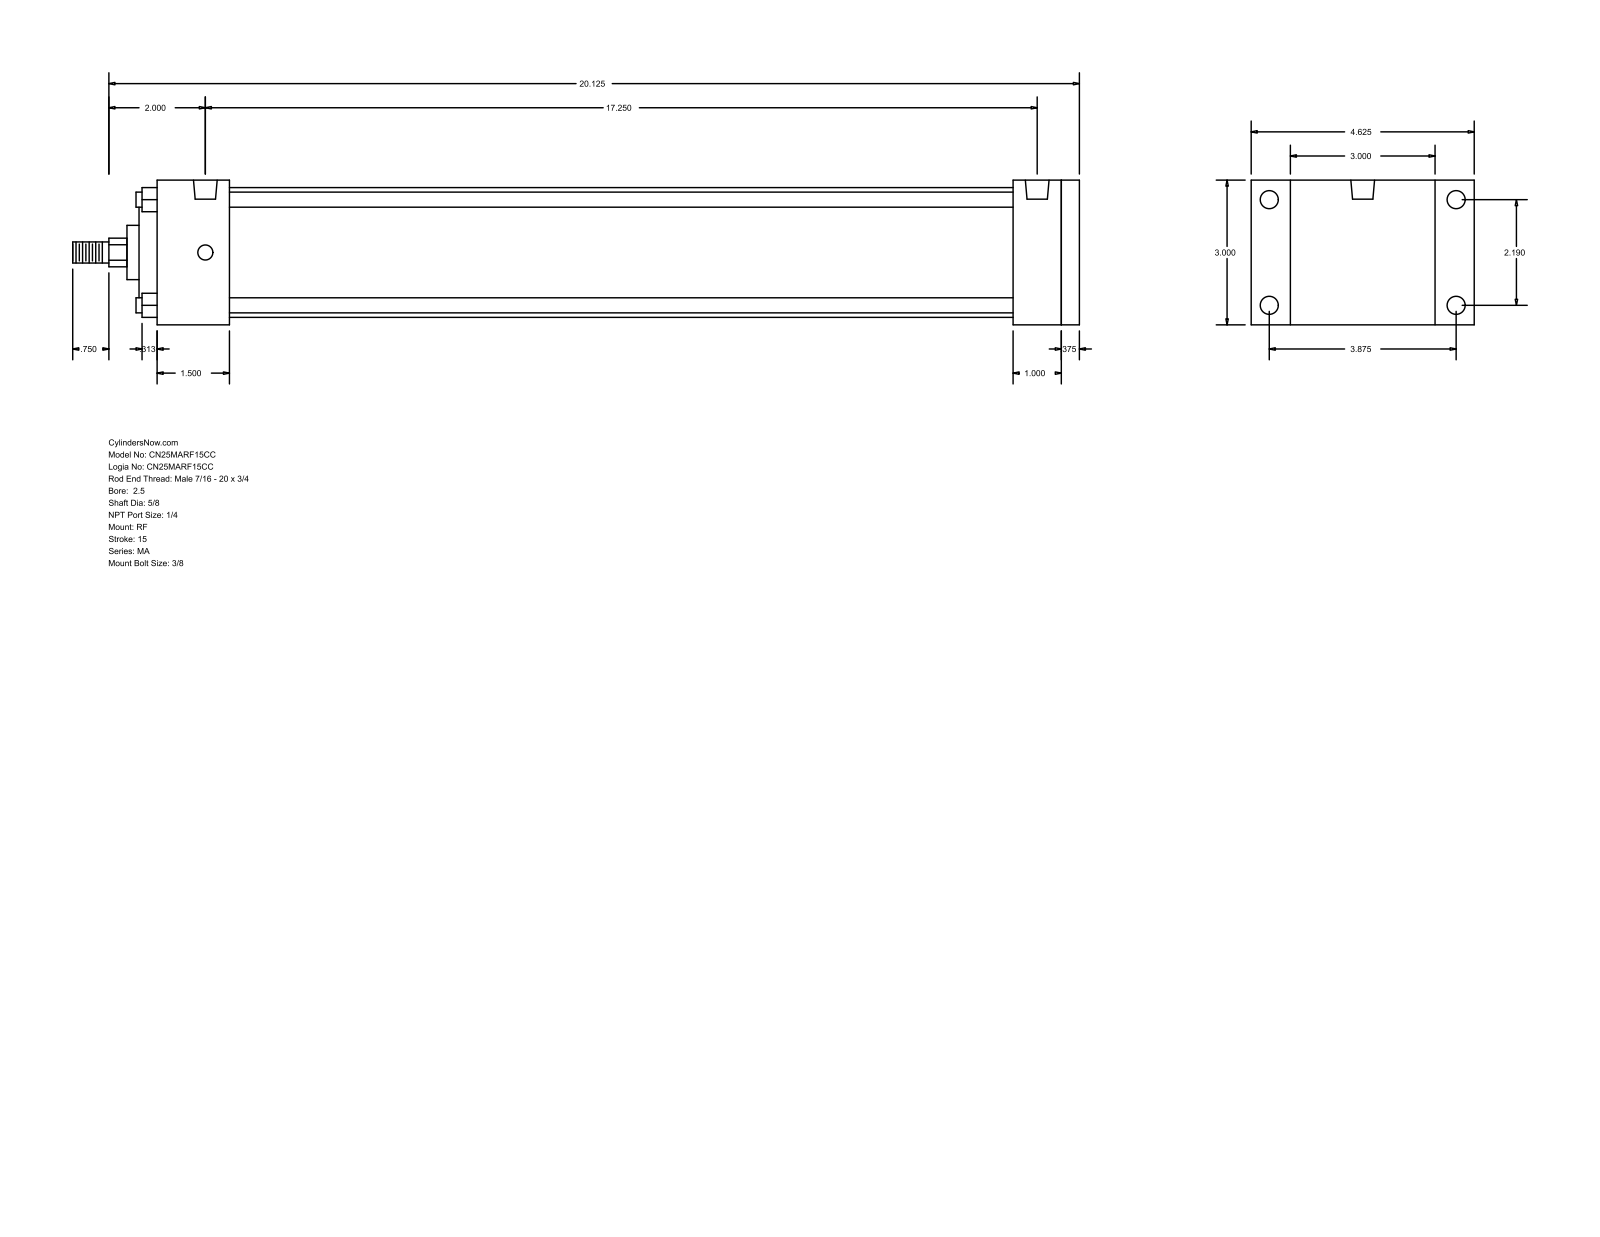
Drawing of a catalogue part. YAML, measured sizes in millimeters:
part_name: "MA_RF__0250_0.625"
step_written_by: "GSSL Pune (CONFIG_CONTROL_DESIGN)"
units: millimeters
bodies: {solids: 0, faces: 94, planar: 65, cylindrical: 29, other: 0}
overall_size: [530.23, 117.47, 76.2]
round_holes:
  - {diameter: 7.94, count: 4}
  - {diameter: 9.53, count: 4}
  - {diameter: 12.49, count: 2}
round_bosses_or_shafts:
  - {diameter: 7.94, count: 4}
  - {diameter: 68.33, count: 1}
  - {diameter: 50.8, count: 1}
  - {diameter: 28.57, count: 1}
  - {diameter: 15.88, count: 1}
  - {diameter: 11.11, count: 1}
partial_cylinders:
  - {radius: 7.54, count: 1}
face_to_face_distances: [76.2, 485.78, 9.53, 476.25, 25.4, 34.93, 38.1, 450.85, 412.75, 438.15]
hole_center_spacings: [55.62, 98.42, 113.05, 438.15]
